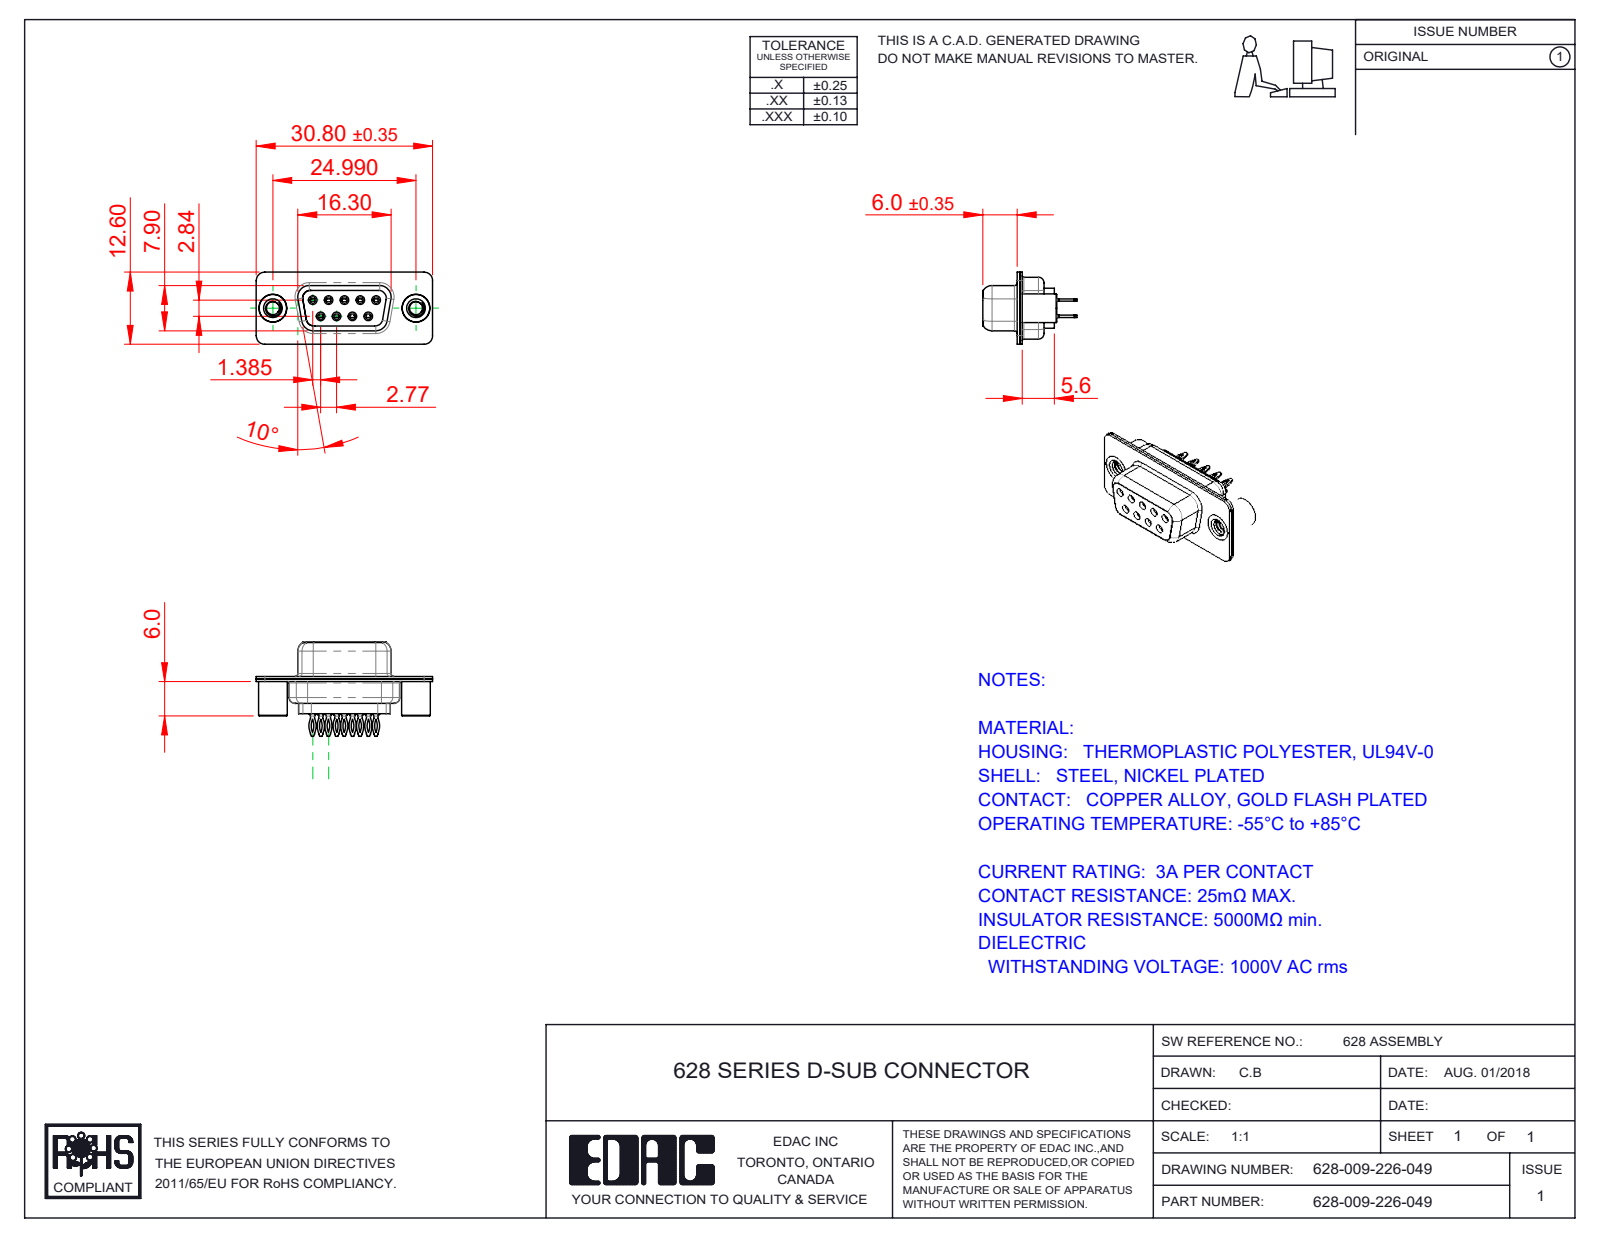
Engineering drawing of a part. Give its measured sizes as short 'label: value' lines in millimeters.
name: 628 Shell Front_09 Contacts; 628-009-226-049; 628 Contact Row 2_26L; 628 4-40 Threaded Standoff BS (+3 more)
written by: SolidWorks 2020 (CONFIG_CONTROL_DESIGN)
unit: mm
bodies: 14 solids, 1210 faces (310 planar, 400 cylindrical, 500 other)
size: 30.8 × 16.45 × 12.6
volume: 1 854 mm³; area: 4 668 mm²
holes: 9× ⌀0.8, 9× ⌀0.9, 9× ⌀1.1, 9× ⌀1.6, 5× ⌀1.7, 2× ⌀2.26, 2× ⌀4, 2× ⌀4.05, 2× ⌀4.85
bosses: 9× ⌀2, 9× ⌀1.5, 9× ⌀1.2, 2× ⌀5, 2× ⌀4.95, 2× ⌀4.8
rounds: 18× R2.92, 18× R3.33, 17× R1.5, 12× R2, 9× R0.28, 6× R1.35, 4× R0.25, 4× R0.5
face distances: 0.45, 0.4, 0.9, 1.9, 8.5, 6.6, 1.4, 6.5, 0.5, 6
hole spacings: 3.16, 2.77, 5.54, 5.03, 5.04, 8.31, 7.48, 7.49
